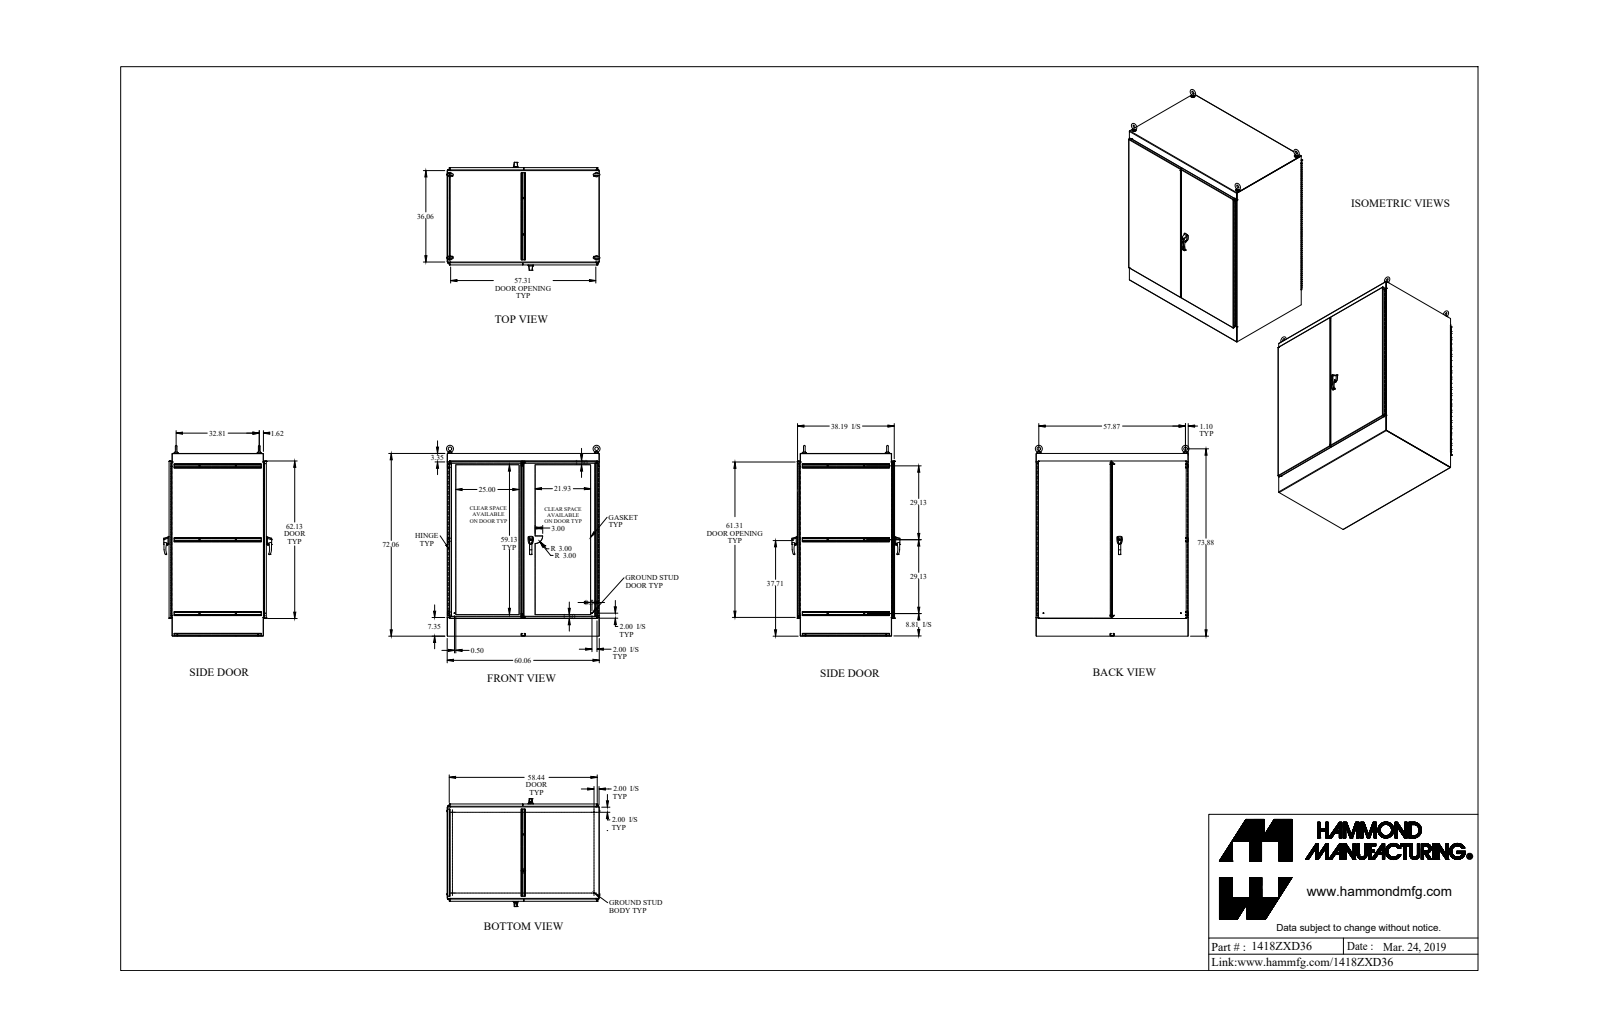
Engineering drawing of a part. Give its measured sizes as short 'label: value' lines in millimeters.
name: 1418ZXD36_Default
written by: SolidWorks 2019 (CONFIG_CONTROL_DESIGN)
unit: mm
bodies: 118 solids, 4680 faces (2090 planar, 2264 cylindrical, 326 other)
size: 1923.1 × 1552.4 × 1082.4
volume: 36 050 000 mm³; area: 29 280 000 mm²
holes: 40× ⌀7.7, 8× ⌀12.7, 4× ⌀2.8, 4× ⌀6.4, 4× ⌀6.5, 4× ⌀7.1, 4× ⌀7.1, 4× ⌀8, 4× ⌀9.9, 4× ⌀10.5, 4× ⌀13.4, 4× ⌀15.9
bosses: 12× ⌀7.1, 8× ⌀6.4, 4× ⌀44.5, 4× ⌀38.1, 4× ⌀31.8, 4× ⌀25.4, 4× ⌀19.1, 4× ⌀18.7
rounds: 54× R1.1, 48× R3.5, 44× R3.2, 40× R1.2, 40× R3.6, 32× R0.5, 16× R1.3, 16× R1.5
face distances: 2.4, 2.4, 972.5, 1523.1, 1827.9, 970.1, 975, 1520.7, 1525.5, 1825.5
hole spacings: 152.4, 304.8, 457.2, 1489.4, 609.6, 1512.6, 762, 1550.5
